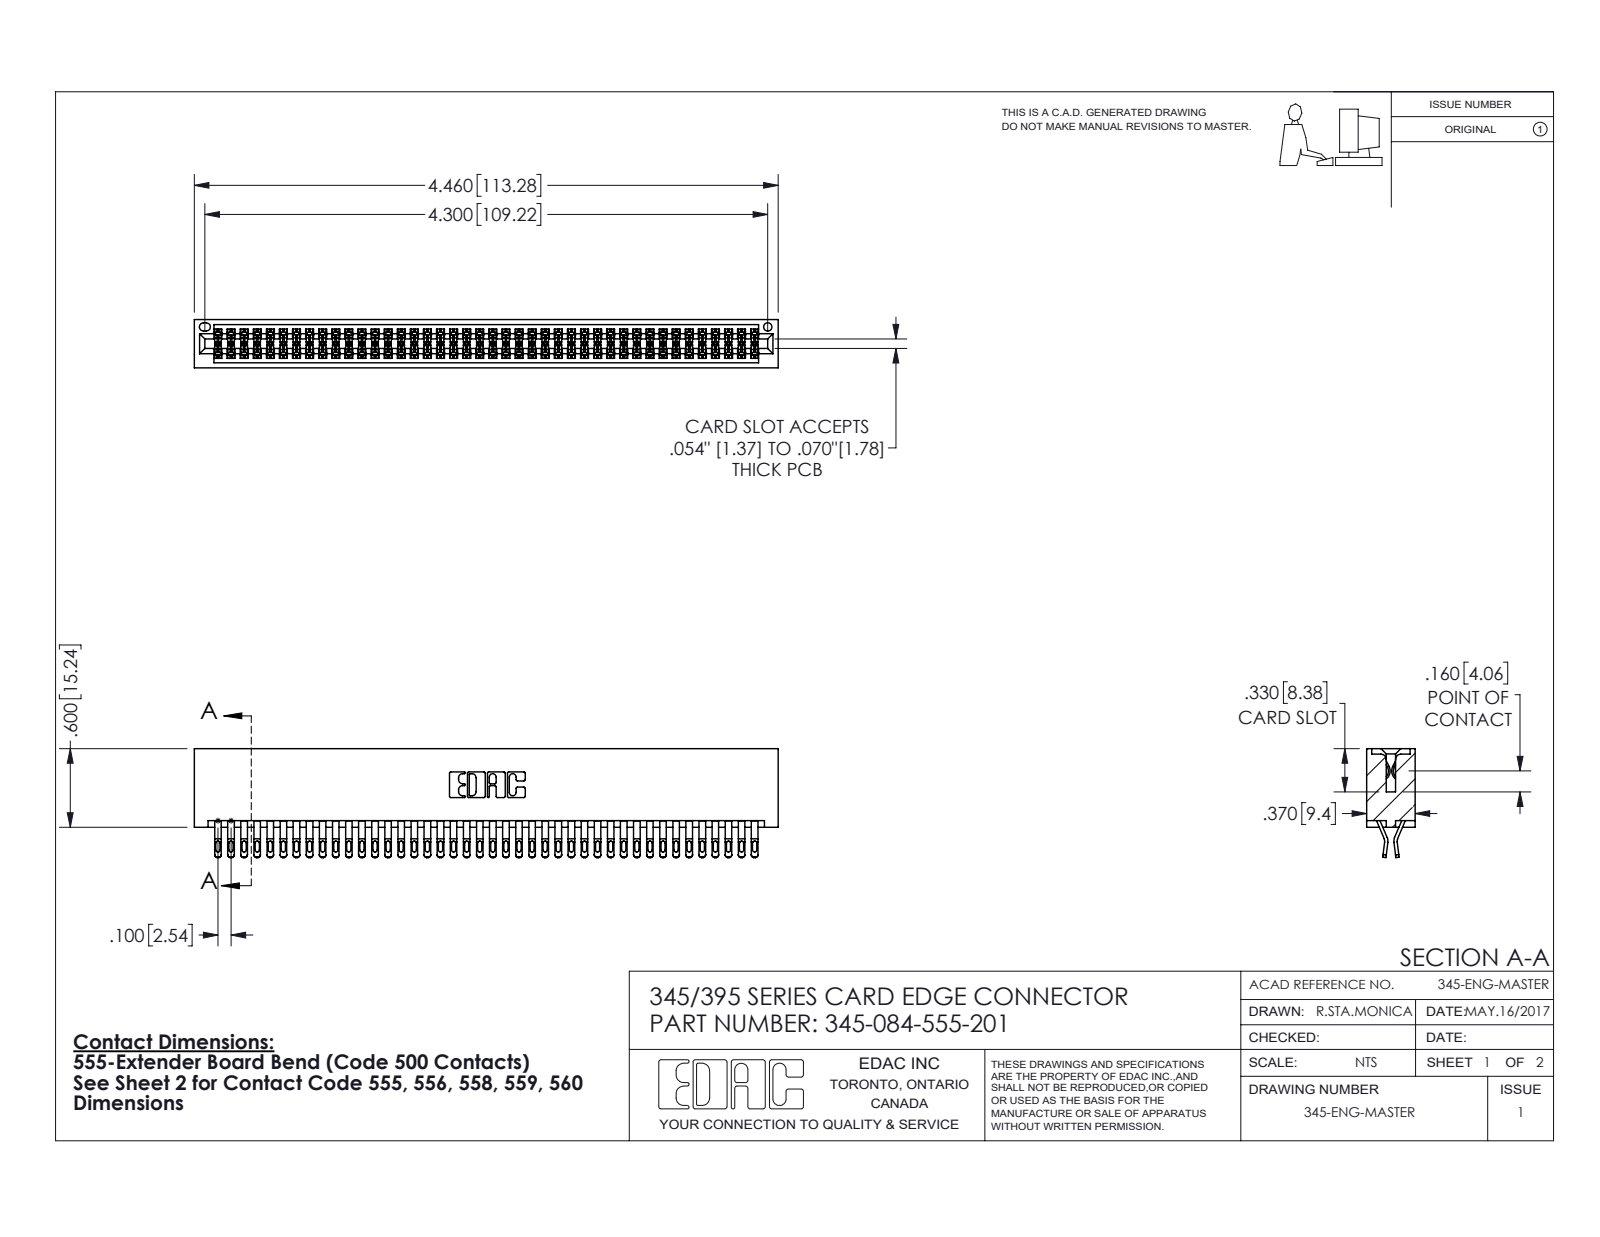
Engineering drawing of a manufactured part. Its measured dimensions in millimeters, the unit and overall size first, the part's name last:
Units: millimetres
Overall size (bounding box): 113.3 × 21.1 × 9.4
Round holes (diameter × count): ⌀1.6 ×1
Partial cylindrical surfaces — rounded edges, fillets, slot ends (radius × count): R0.4 ×210, R0.5 ×168, R0.2 ×126, R0.3 ×22, R0.2 ×6, R0.8 ×6, R0.7 ×3, R0.3 ×2
Main face-to-face distances: 7.6, 1.8, 0.6, 5.1, 9.4, 2.5, 6.9, 5.7, 4.4, 3.8
Volume: 11 900 mm³ · Surface area: 18 690 mm²
Bodies: 85 solids, 4822 faces (2680 planar, 2142 cylindrical, 0 other)
Part name (STEP PRODUCT): 345-084-555-201; 345-292-001_555 Tail; 345 Part_No Mounting Lugs
STEP written by: SolidWorks 2016 (CONFIG_CONTROL_DESIGN)
